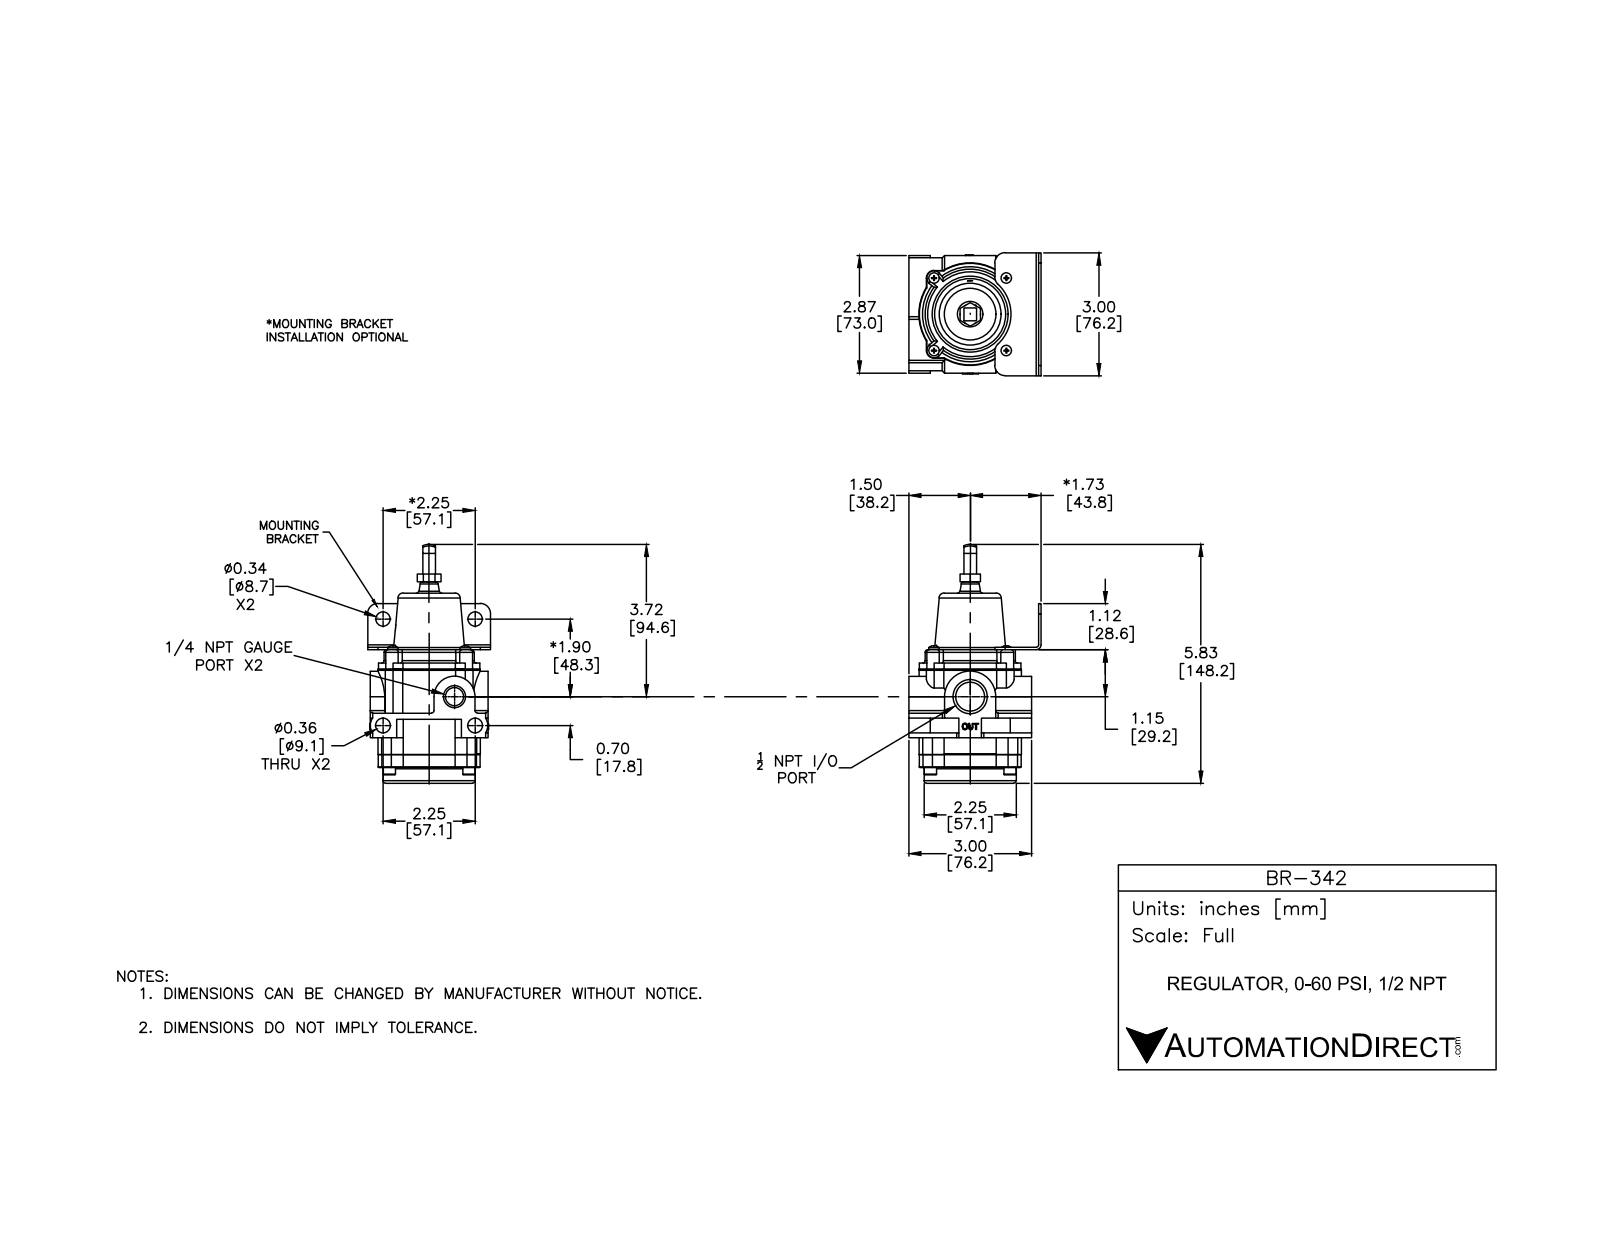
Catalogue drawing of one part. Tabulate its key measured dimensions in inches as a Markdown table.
| quantity | value |
| --- | --- |
| part name | BR-342 |
| STEP written by | SolidWorks 2015 (CONFIG_CONTROL_DESIGN) |
| units | inches |
| bodies | 13 solids, 1491 faces (287 planar, 973 cylindrical, 231 other) |
| overall size | 5.937 × 3 × 2.895 |
| volume | 20.19 in³ |
| surface area | 103.4 in² |
| round holes (diameter × count) | 0.159 × 8, 0.201 × 4, 0.207 × 4, 0.36 × 2, 0.125 × 1, 0.257 × 1, 0.438 × 1, 0.703 × 1 |
| round bosses / shafts (diameter × count) | 0.19 × 8, 0.149 × 8, 0.312 × 5, 0.373 × 4, 2.25 × 1, 0.512 × 1, 0.203 × 1 |
| partial cylindrical surfaces (radius × count) | 0.004 × 48, 0.188 × 12, 0.02 × 6, 0.062 × 5, 0.063 × 5, 0.187 × 4, 0.313 × 2, 0.5 × 1 |
| main face-to-face distances | 2.075, 0.711, 2.786, 1.126, 0.415, 1.66, 1.18, 1.21, 1.726, 1.015 |
| hole center spacings | 1.858, 0.125, 1.944, 1.375, 1.25, 1.25, 1.768, 1.768 |
